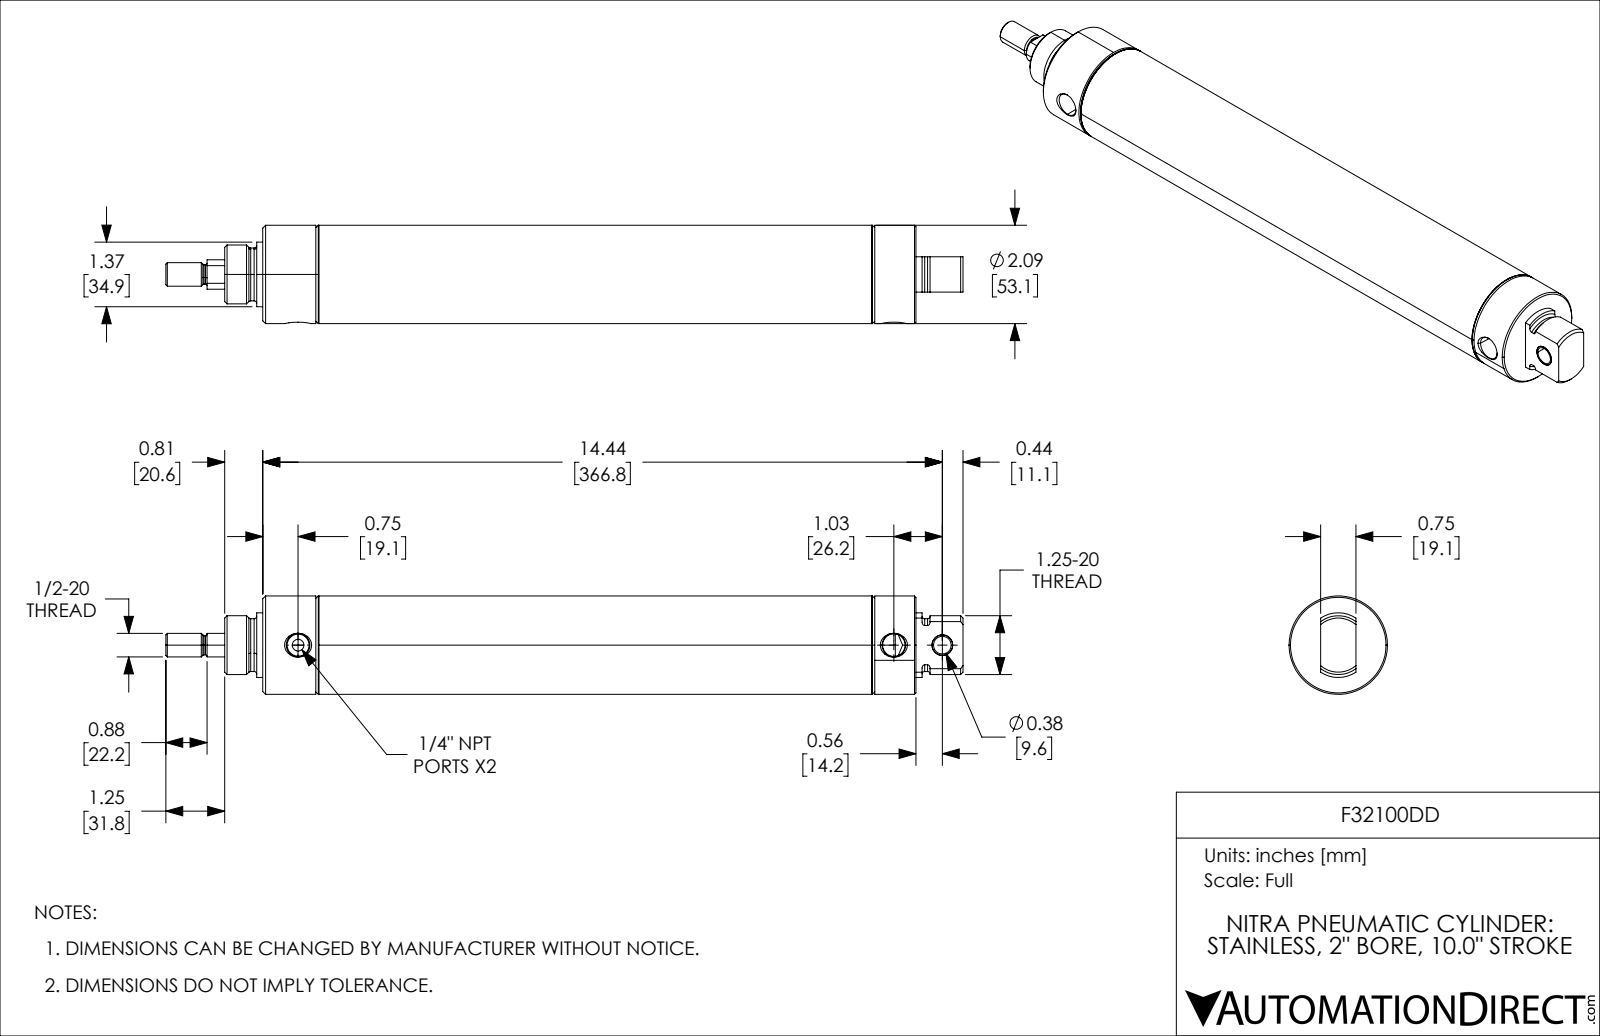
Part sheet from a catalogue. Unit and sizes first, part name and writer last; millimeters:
Units: millimetres
Overall size (bounding box): 430.23 × 53.09 × 53.09
Round holes (diameter × count): ⌀6.35 ×1, ⌀9.55 ×1, ⌀11.15 ×1, ⌀12.18 ×1, ⌀16.52 ×1, ⌀19.05 ×1, ⌀49.05 ×1
Round bosses / shafts (diameter × count): ⌀53.09 ×1, ⌀51.16 ×1, ⌀34.87 ×1, ⌀31.75 ×1, ⌀28.51 ×1, ⌀15.88 ×1, ⌀12.7 ×1, ⌀10.46 ×1
Partial cylindrical surfaces — rounded edges, fillets, slot ends (radius × count): R14.25 ×1
Main face-to-face distances: 30.17, 254, 284.17, 314.4, 60.4, 30.23, 284.18, 30.18, 30.22, 38.15
Hole centre spacings: 26.16, 321.56, 347.72
Volume: 326 180 mm³ · Surface area: 157 901 mm²
Bodies: 5 solids, 160 faces (31 planar, 60 cylindrical, 69 other)
Part name (STEP PRODUCT): F32100DD_7; F32100DD_9; F32100DD_11; F32100DD_3 (+2 more)
STEP written by: SolidWorks 2021 (CONFIG_CONTROL_DESIGN)
